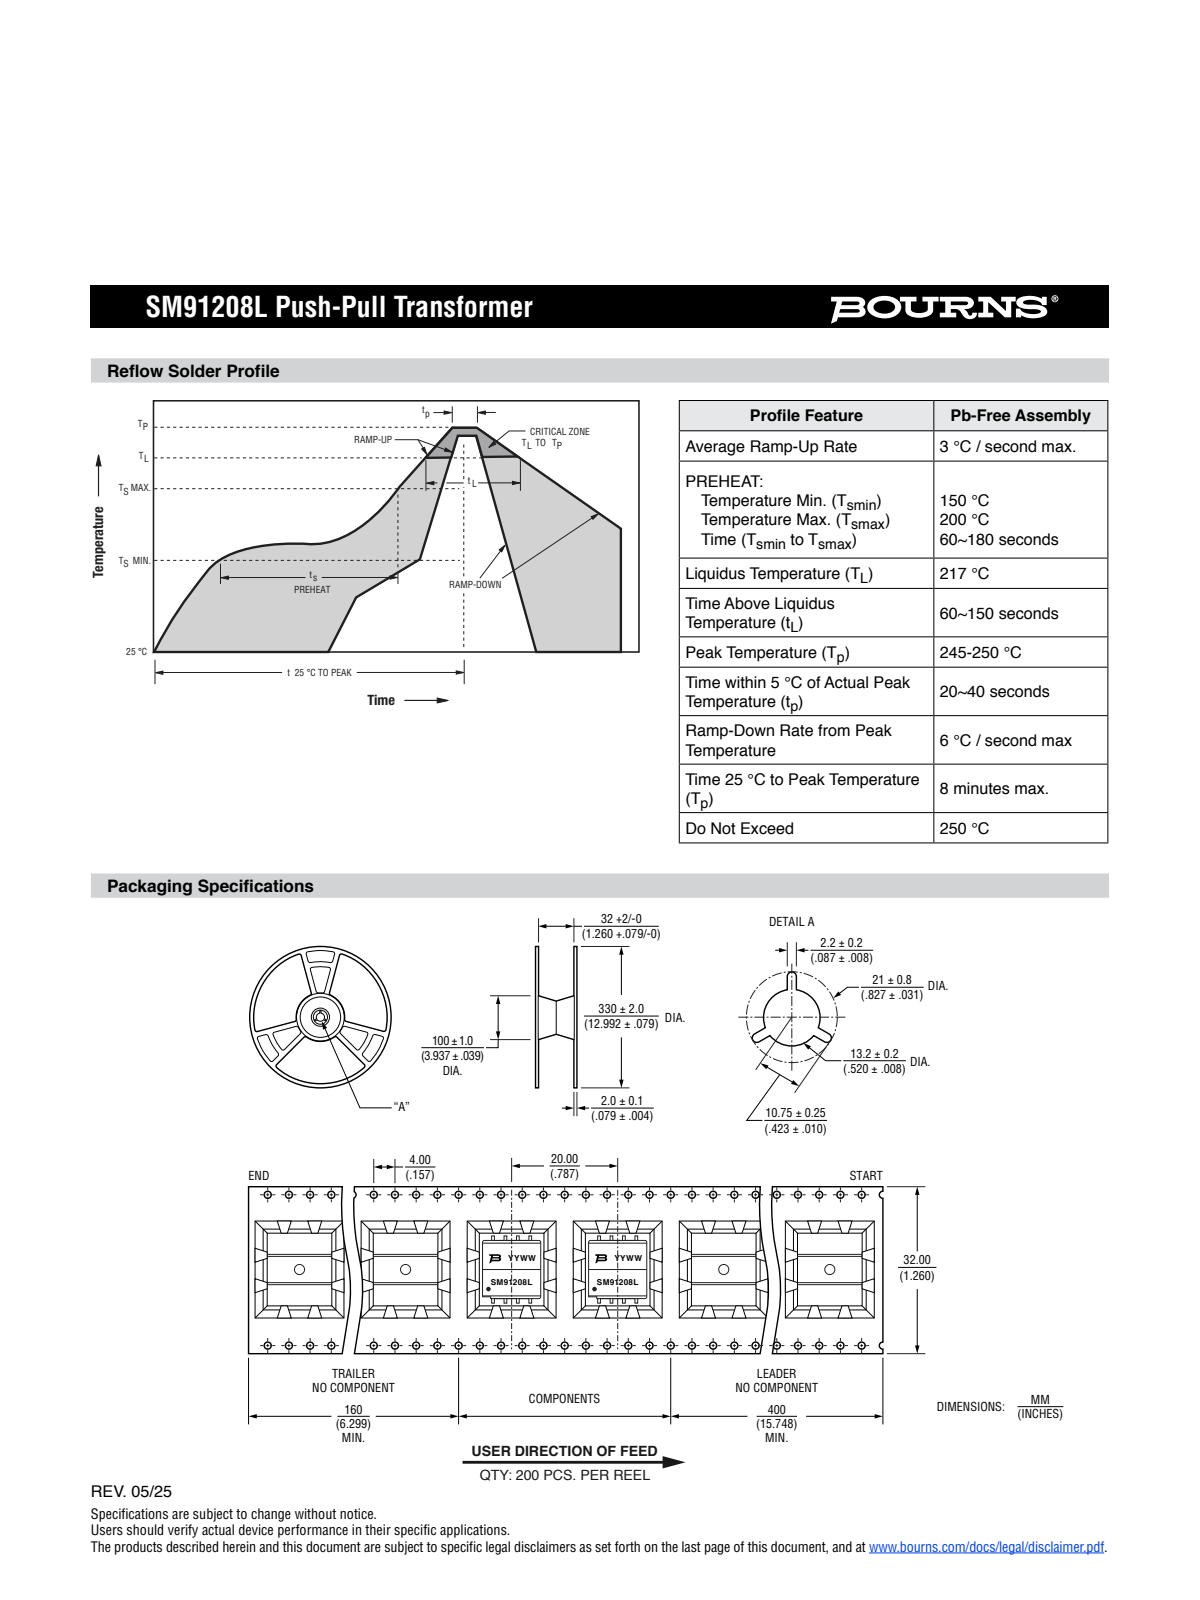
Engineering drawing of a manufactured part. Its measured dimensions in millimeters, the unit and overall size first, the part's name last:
Units: millimetres
Overall size (bounding box): 13.2 × 11.8 × 11.62
Round bosses / shafts (diameter × count): ⌀1 ×1
Partial cylindrical surfaces — rounded edges, fillets, slot ends (radius × count): R0.3 ×25, R0.2 ×22, R0.15 ×2, R0.65 ×2, R0.12 ×1, R0.13 ×1, R0.42 ×1, R0.46 ×1
Main face-to-face distances: 7.65, 10.4, 11.8, 0.5, 10, 2.1, 2.35, 7.9, 10.9, 2.3
Volume: 1 083 mm³ · Surface area: 892 mm²
Bodies: 1 solid, 421 faces (232 planar, 85 cylindrical, 104 other)
Part name (STEP PRODUCT): SM91208L
STEP written by: Autodesk Inventor 2023 (AUTOMOTIVE_DESIGN)
